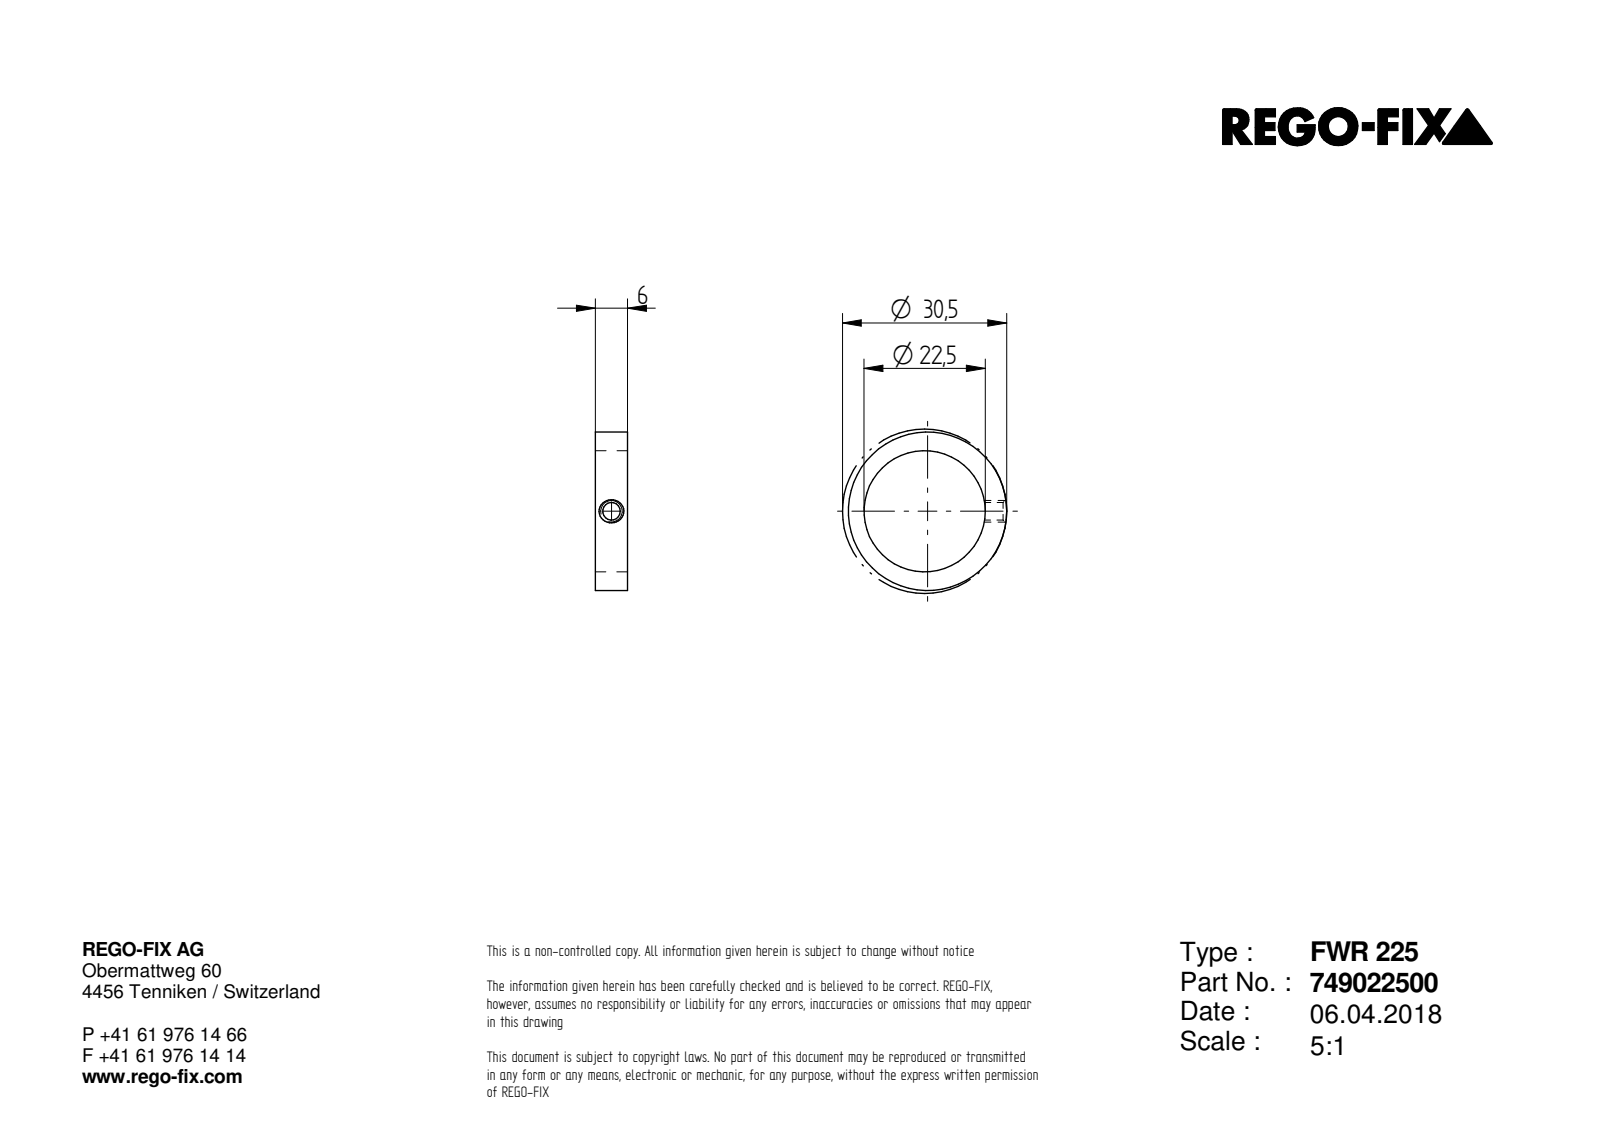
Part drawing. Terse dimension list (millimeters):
written by: Unknown (AUTOMOTIVE_DESIGN)
unit: mm
bodies: 1 solid, 6 faces (2 planar, 3 cylindrical, 1 other)
size: 29.4 × 29.4 × 6
volume: 1 652 mm³; area: 1 562 mm²
holes: 1× ⌀3.24, 1× ⌀22.5
bosses: 1× ⌀29.4
face distances: 6
